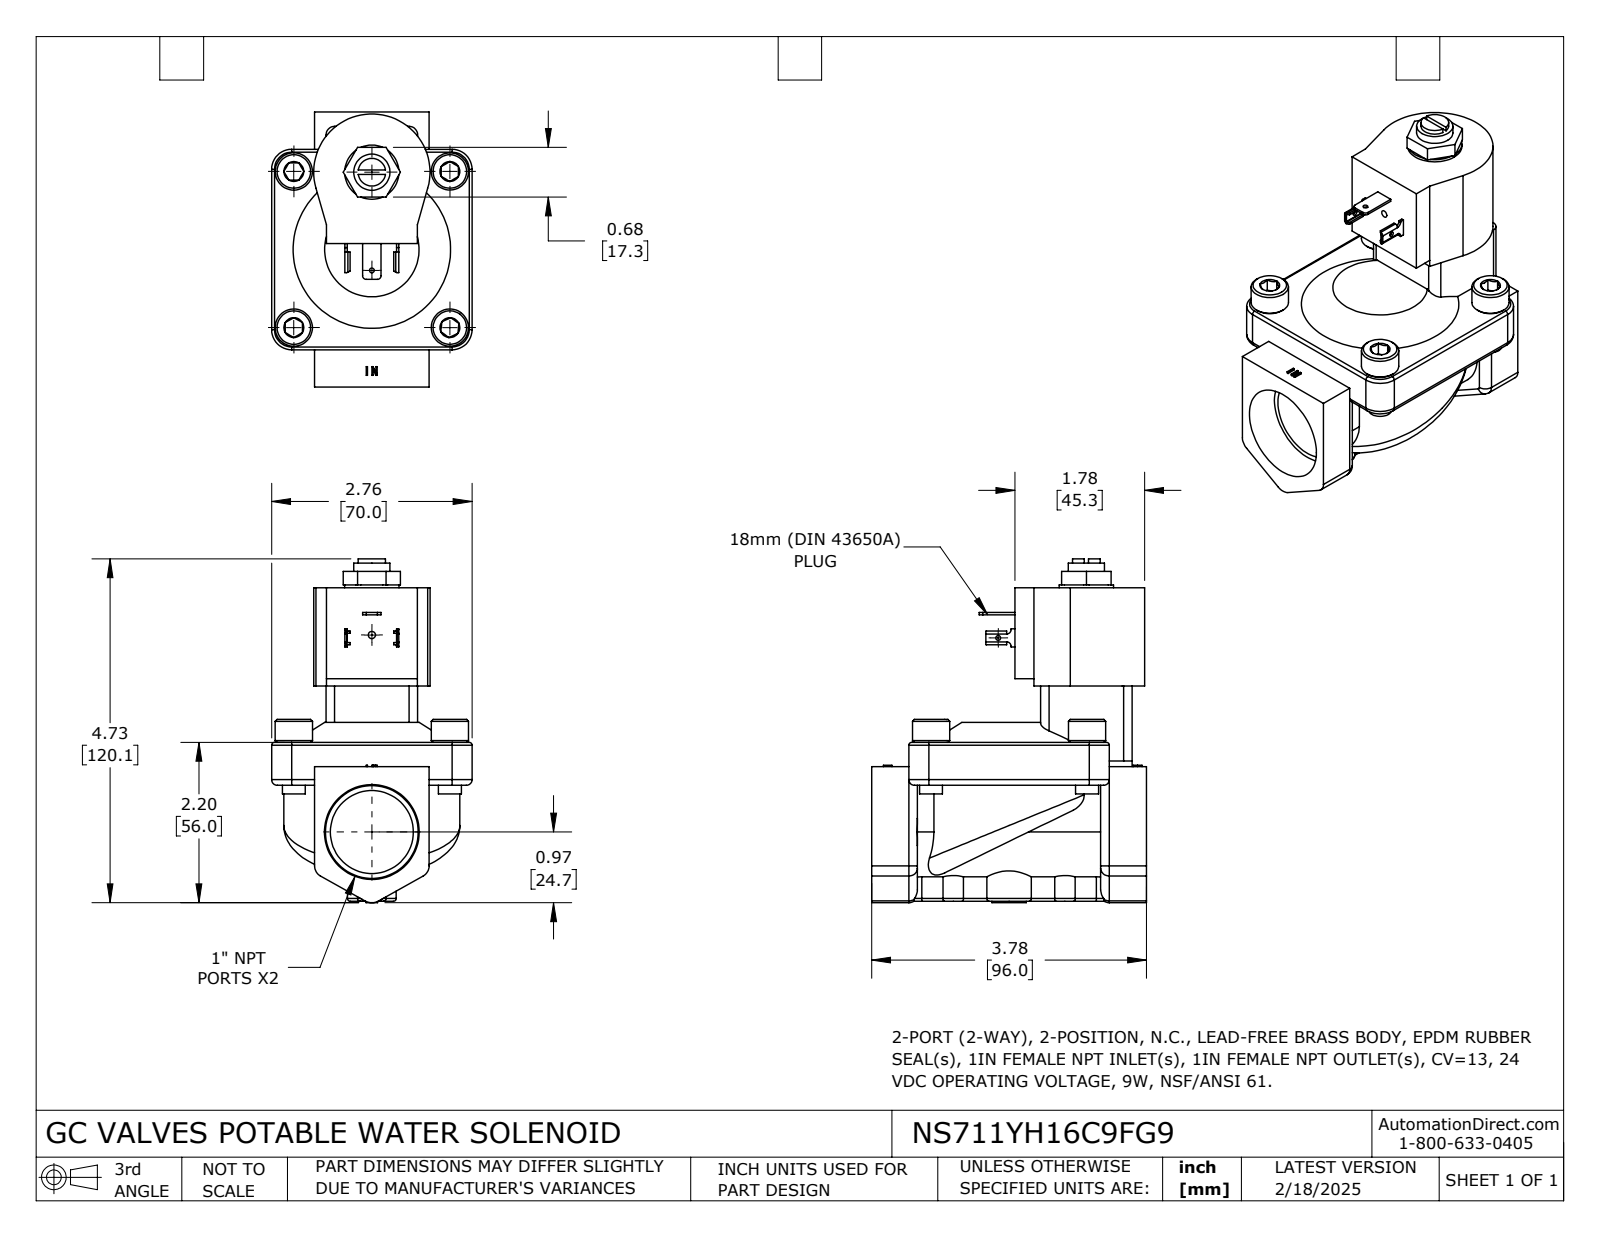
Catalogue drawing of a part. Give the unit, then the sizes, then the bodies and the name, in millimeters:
Units: millimetres
Overall size (bounding box): 120.07 × 96 × 70
Round holes (diameter × count): ⌀1.68 ×1, ⌀1.7 ×1, ⌀2.53 ×1, ⌀28.98 ×1
Round bosses / shafts (diameter × count): ⌀13 ×4, ⌀8 ×4, ⌀18.95 ×1, ⌀12.67 ×1, ⌀9.65 ×1
Partial cylindrical surfaces — rounded edges, fillets, slot ends (radius × count): R3 ×12, R1 ×6, R0.15 ×4, R1.04 ×4, R2 ×4, R7 ×4, R5 ×3, R1.27 ×2
Main face-to-face distances: 15, 4, 36, 19, 51, 55, 53.99, 7, 32, 6.5
Hole centre spacings: 68.76
Volume: 261 303 mm³ · Surface area: 42 835 mm²
Bodies: 1 solid, 412 faces (199 planar, 115 cylindrical, 98 other)
Part name (STEP PRODUCT): NS711YH16C9FG9
STEP written by: SolidWorks 2024 (CONFIG_CONTROL_DESIGN)
